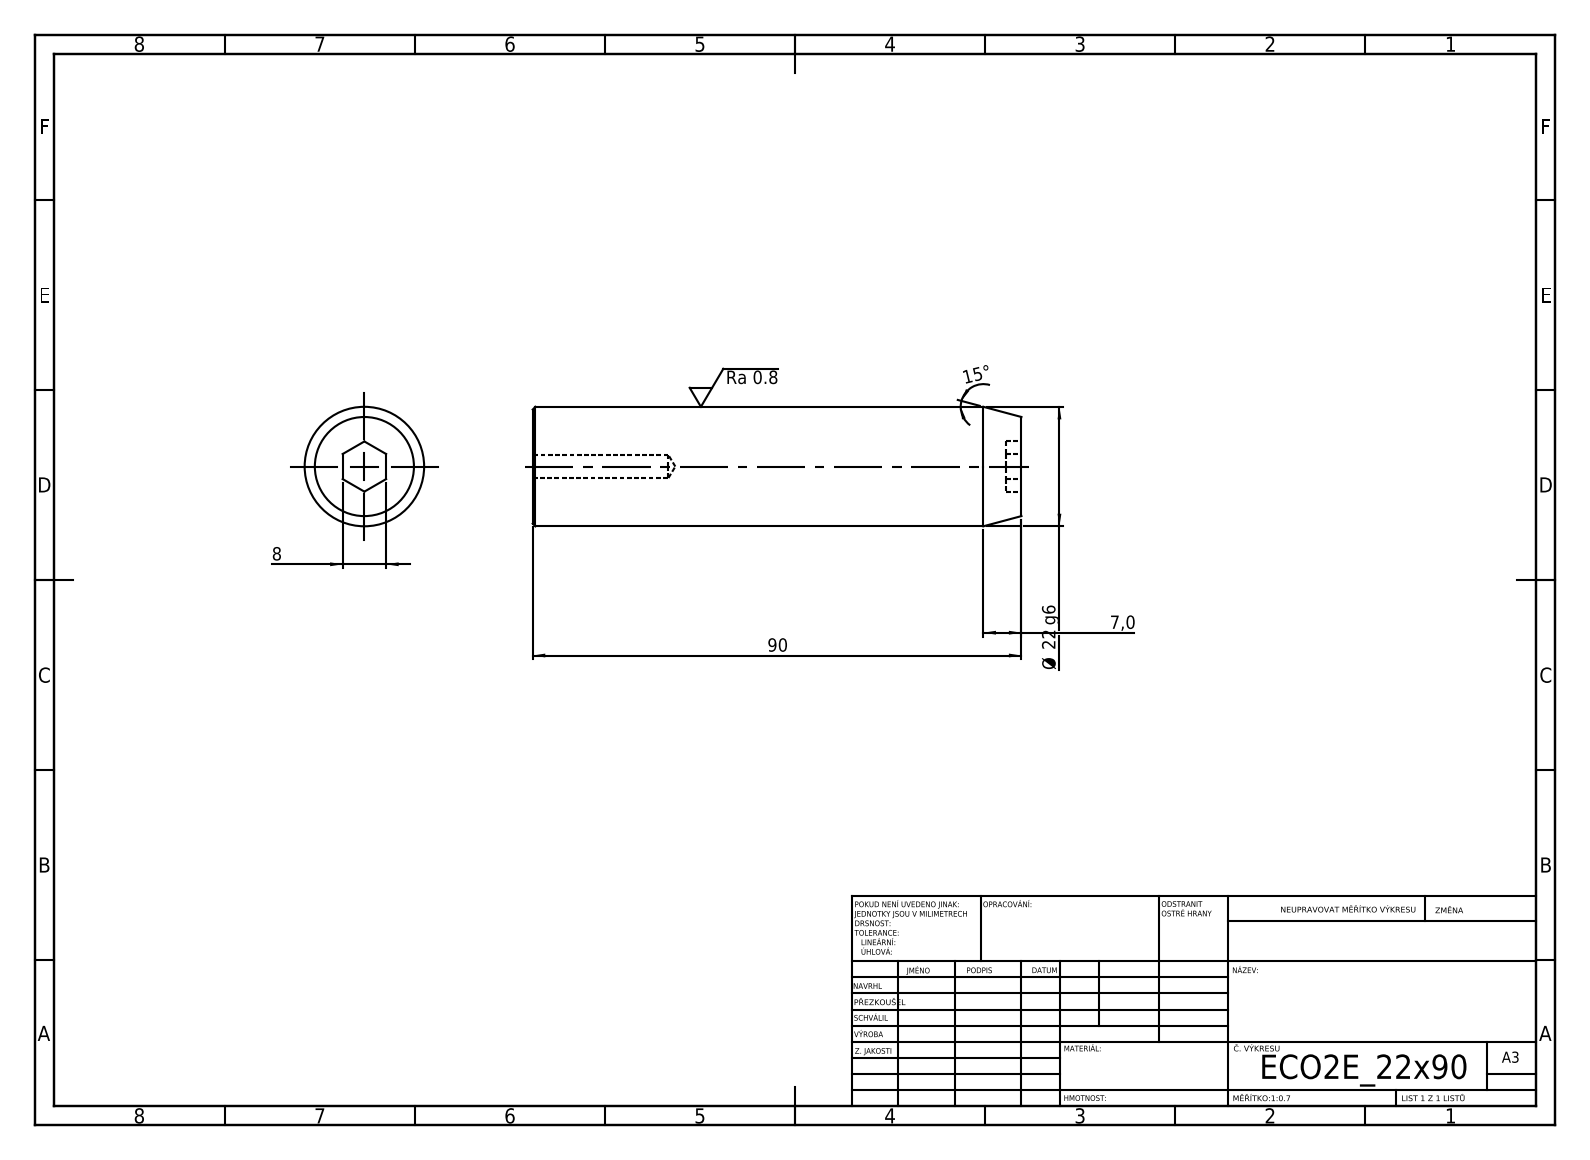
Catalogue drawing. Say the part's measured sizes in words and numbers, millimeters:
Its 3-D file was written by "SolidWorks 2019 (CONFIG_CONTROL_DESIGN)". It is 1 solid with 19 faces: 9 planar, 4 cylindrical and 6 other. Overall it measures 90 by 22 by 22 millimeters. Its volume is 33 268 cubic millimeters and its surface area 7 226 square millimeters. Round holes: 1 of diameter 4.2. Round bosses or shafts: 1 of diameter 22. The main face-to-face distances are 90, 2.8, 87.2, 8.
